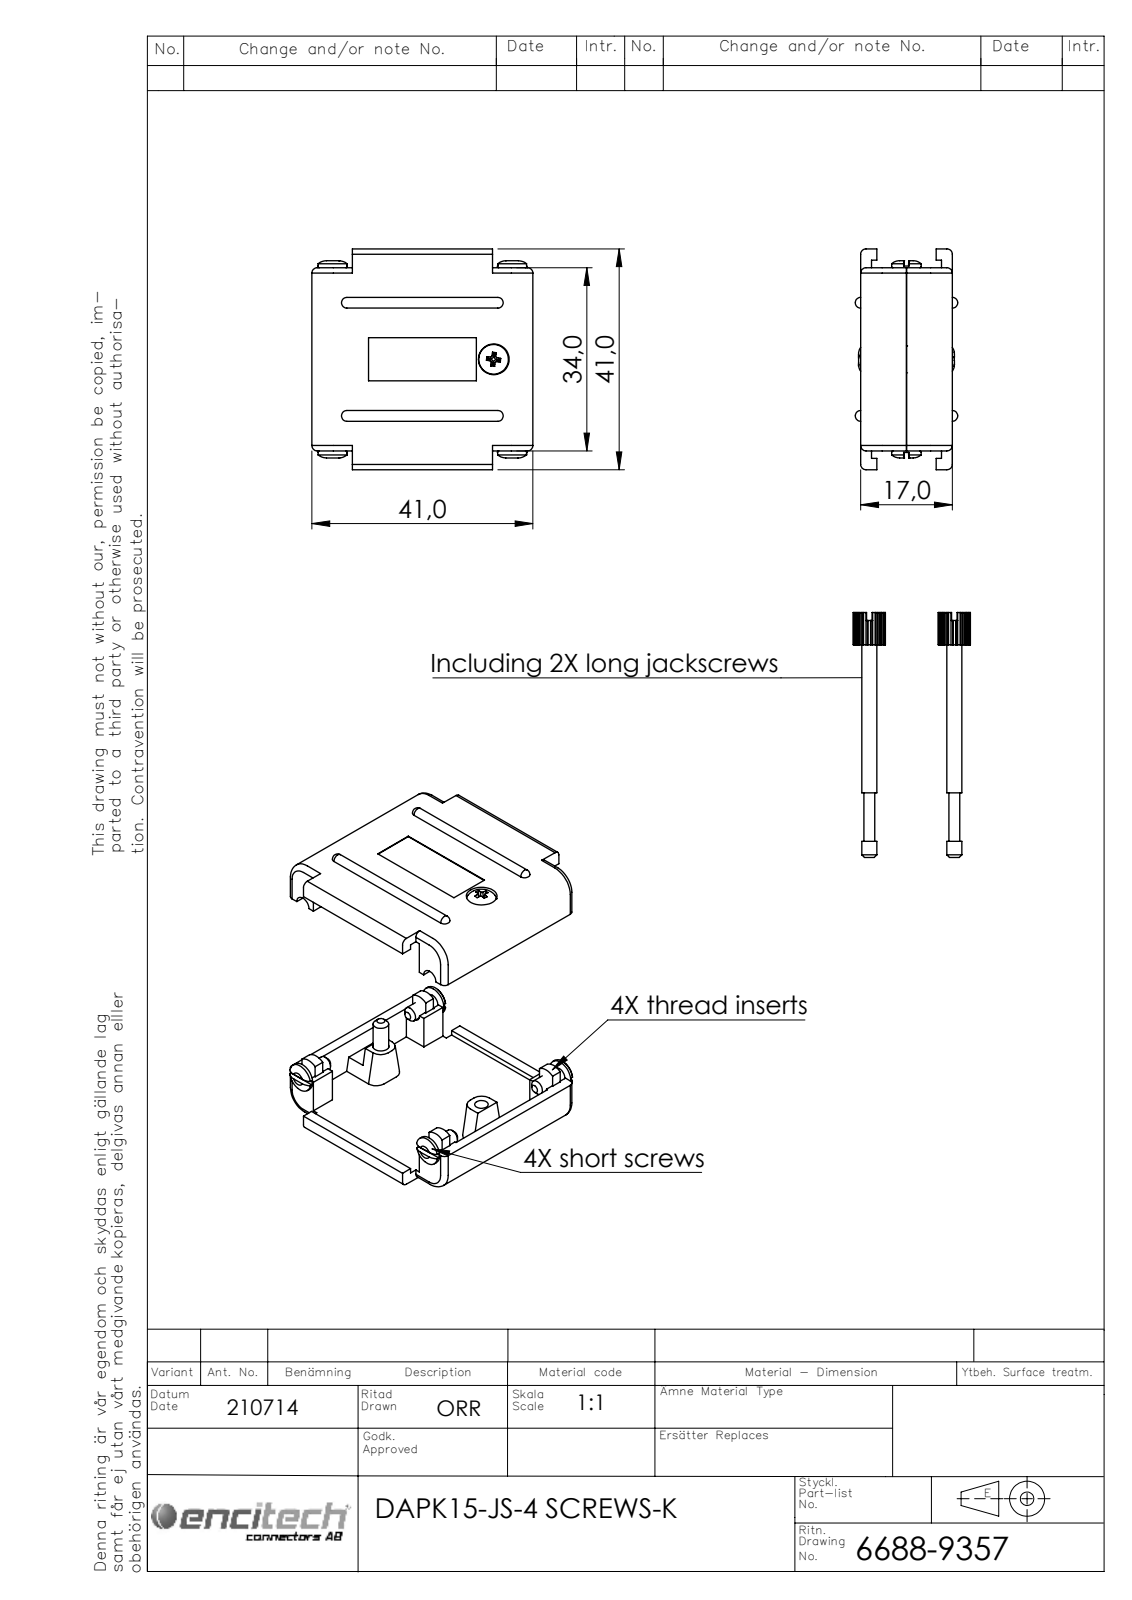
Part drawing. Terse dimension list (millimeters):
name: 6859-0105-02; 6688-9357; 6811-0106-01; 6855-0108-01 (+1 more)
written by: SolidWorks 2021 (AUTOMOTIVE_DESIGN)
unit: mm
bodies: 12 solids, 398 faces (218 planar, 104 cylindrical, 76 other)
size: 41 × 41 × 19.4
volume: 9 973 mm³; area: 11 384 mm²
holes: 4× ⌀2.5, 2× ⌀3, 2× ⌀3.2, 2× ⌀5.7
bosses: 2× ⌀5.5, 2× ⌀5.45, 2× ⌀2.9, 2× ⌀2.8
rounds: 16× R1, 4× R4, 2× R2.85
face distances: 2, 15, 13, 8.5, 17, 6.5, 39, 3.5, 41, 1.9
hole spacings: 33.3, 26.45, 26.4, 26.5
